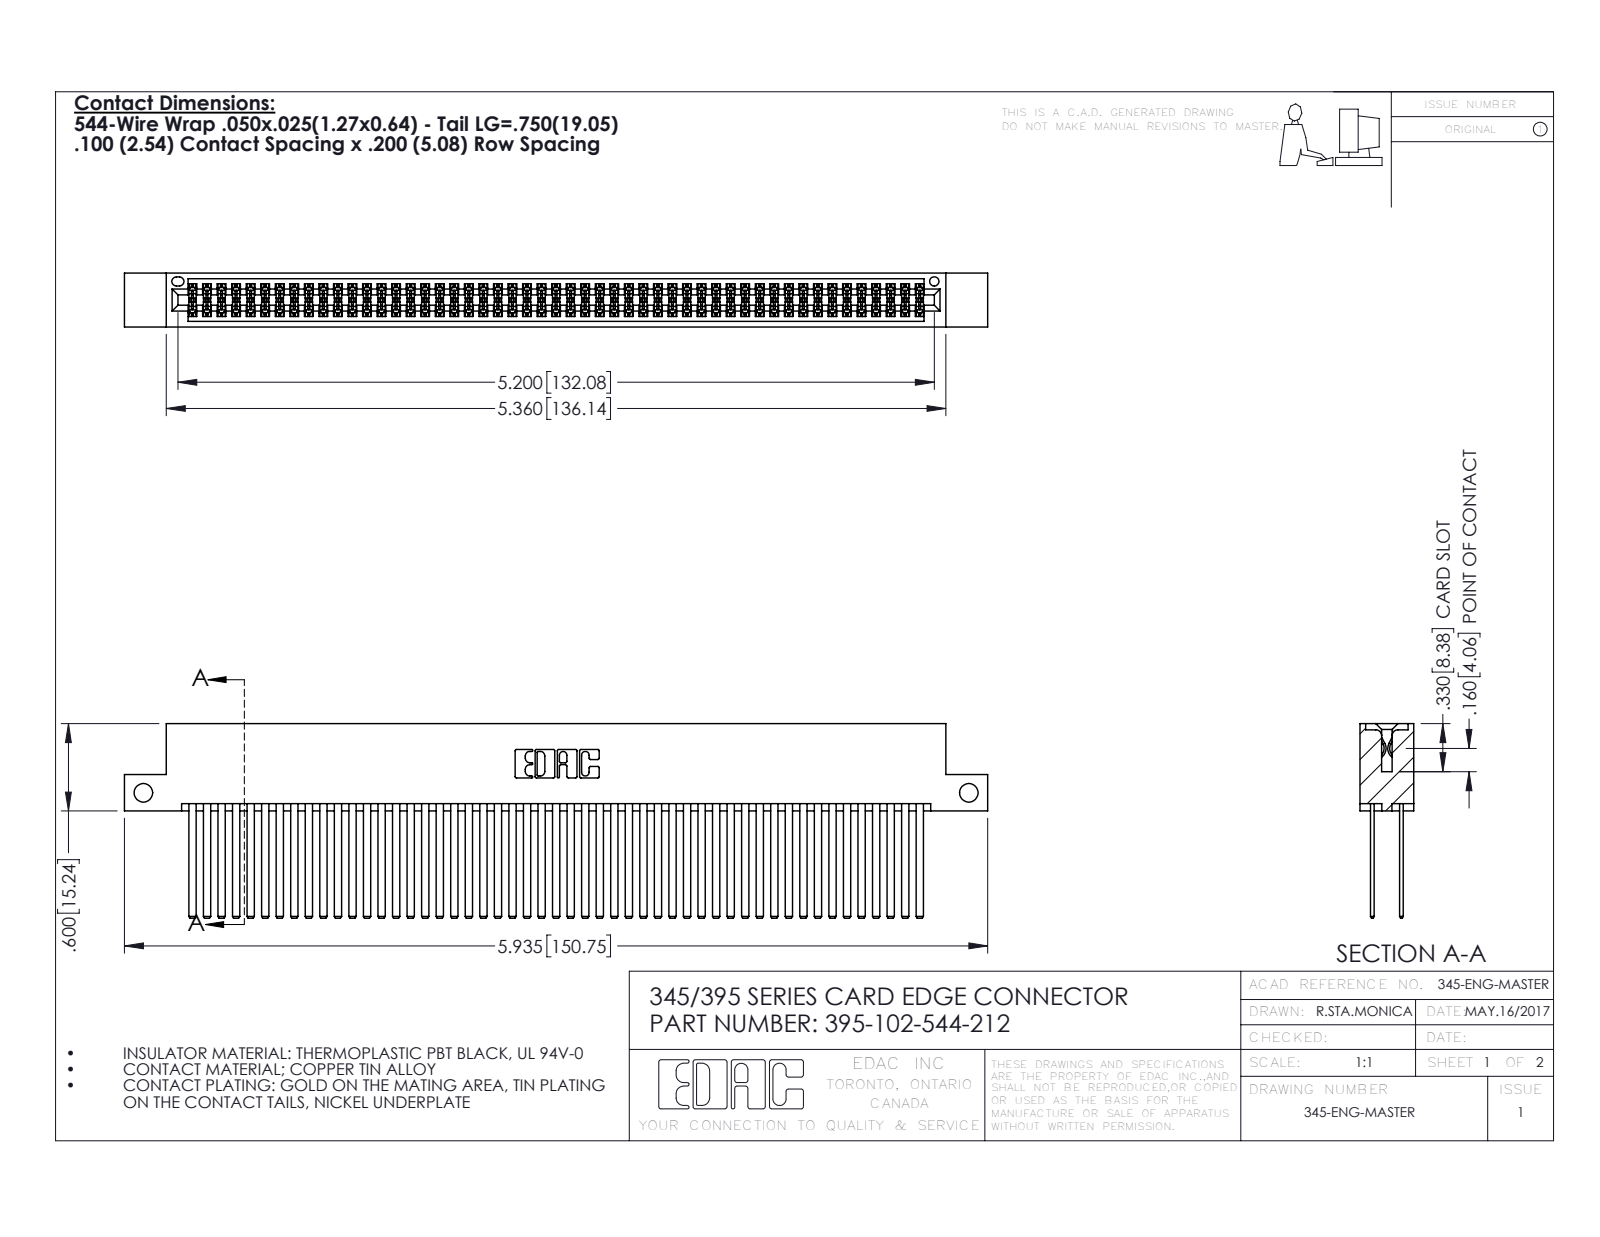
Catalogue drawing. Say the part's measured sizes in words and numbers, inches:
The part is named "345 Part_Flush Mounting Lugs - Side Mount; 345-292-001_345-293-144; 395-102-544-212". Its 3-D file was written by "SolidWorks 2016 (CONFIG_CONTROL_DESIGN)". It is 103 solids with 4614 faces: 3038 planar, 1576 cylindrical and 0 other. Overall it measures 5.935 by 1.337 by 0.37 inches. Its volume is 0.981 cubic inches and its surface area 43.37 square inches. Round holes: 2 of diameter 0.128, 1 of diameter 0.064. Partial cylindrical surfaces (rounded edges, fillets, slot ends): 153 of radius 0.006, 22 of radius 0.01, 6 of radius 0.007, 6 of radius 0.031, 3 of radius 0.026, 2 of radius 0.014, 2 of radius 0.019, 2 of radius 0.022. The main face-to-face distances are 0.2, 0.025, 0.298, 0.072, 0.098, 0.272, 0.225, 0.175, 0.37, 0.05. The hole center spacings are 5.675.
